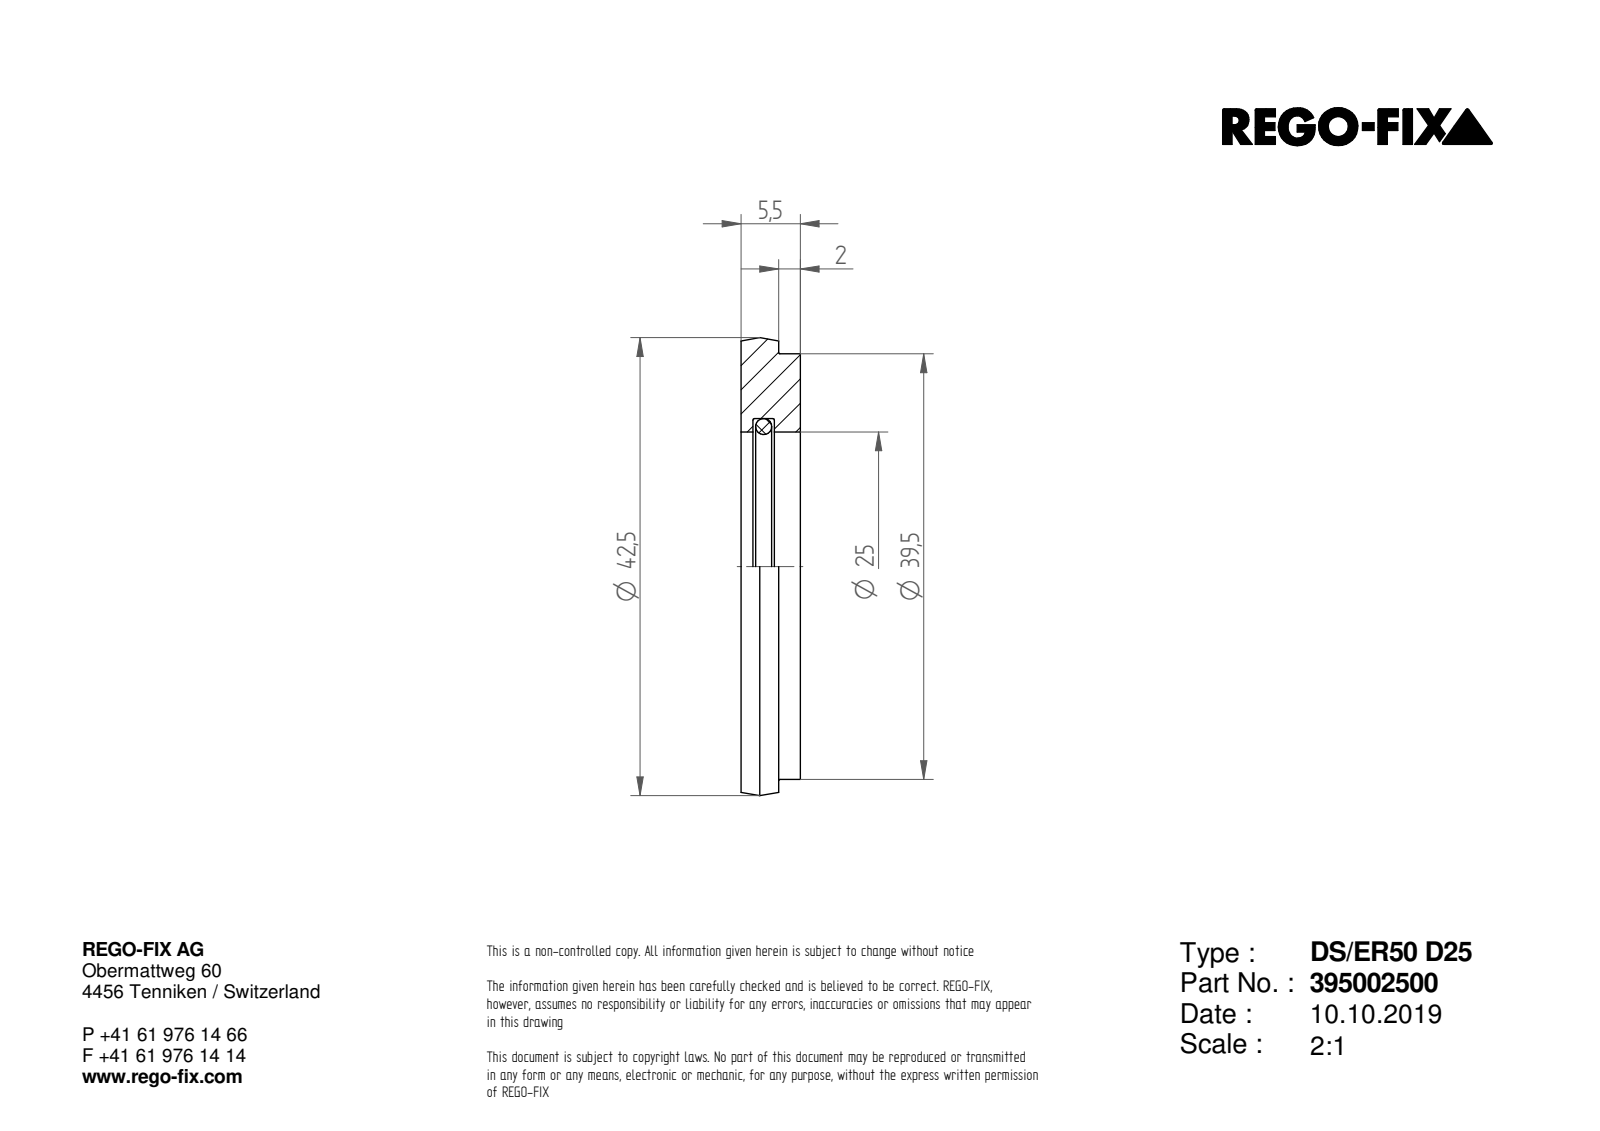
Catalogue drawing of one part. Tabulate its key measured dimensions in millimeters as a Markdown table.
| quantity | value |
| --- | --- |
| part name | NOCUT |
| STEP written by | SIEMENS PLM Software Solid Edge ST10 (AUTOMOTIVE_DESIGN) |
| units | millimeters |
| bodies | 1 solid, 7 faces (3 planar, 3 cylindrical, 1 other) |
| overall size | 42.5 × 42.5 × 5.5 |
| volume | 4 716 mm³ |
| surface area | 2 998 mm² |
| round holes (diameter × count) | 25 × 1 |
| round bosses / shafts (diameter × count) | 42.5 × 1, 39.5 × 1 |
| main face-to-face distances | 5.5, 2, 3.5 |
